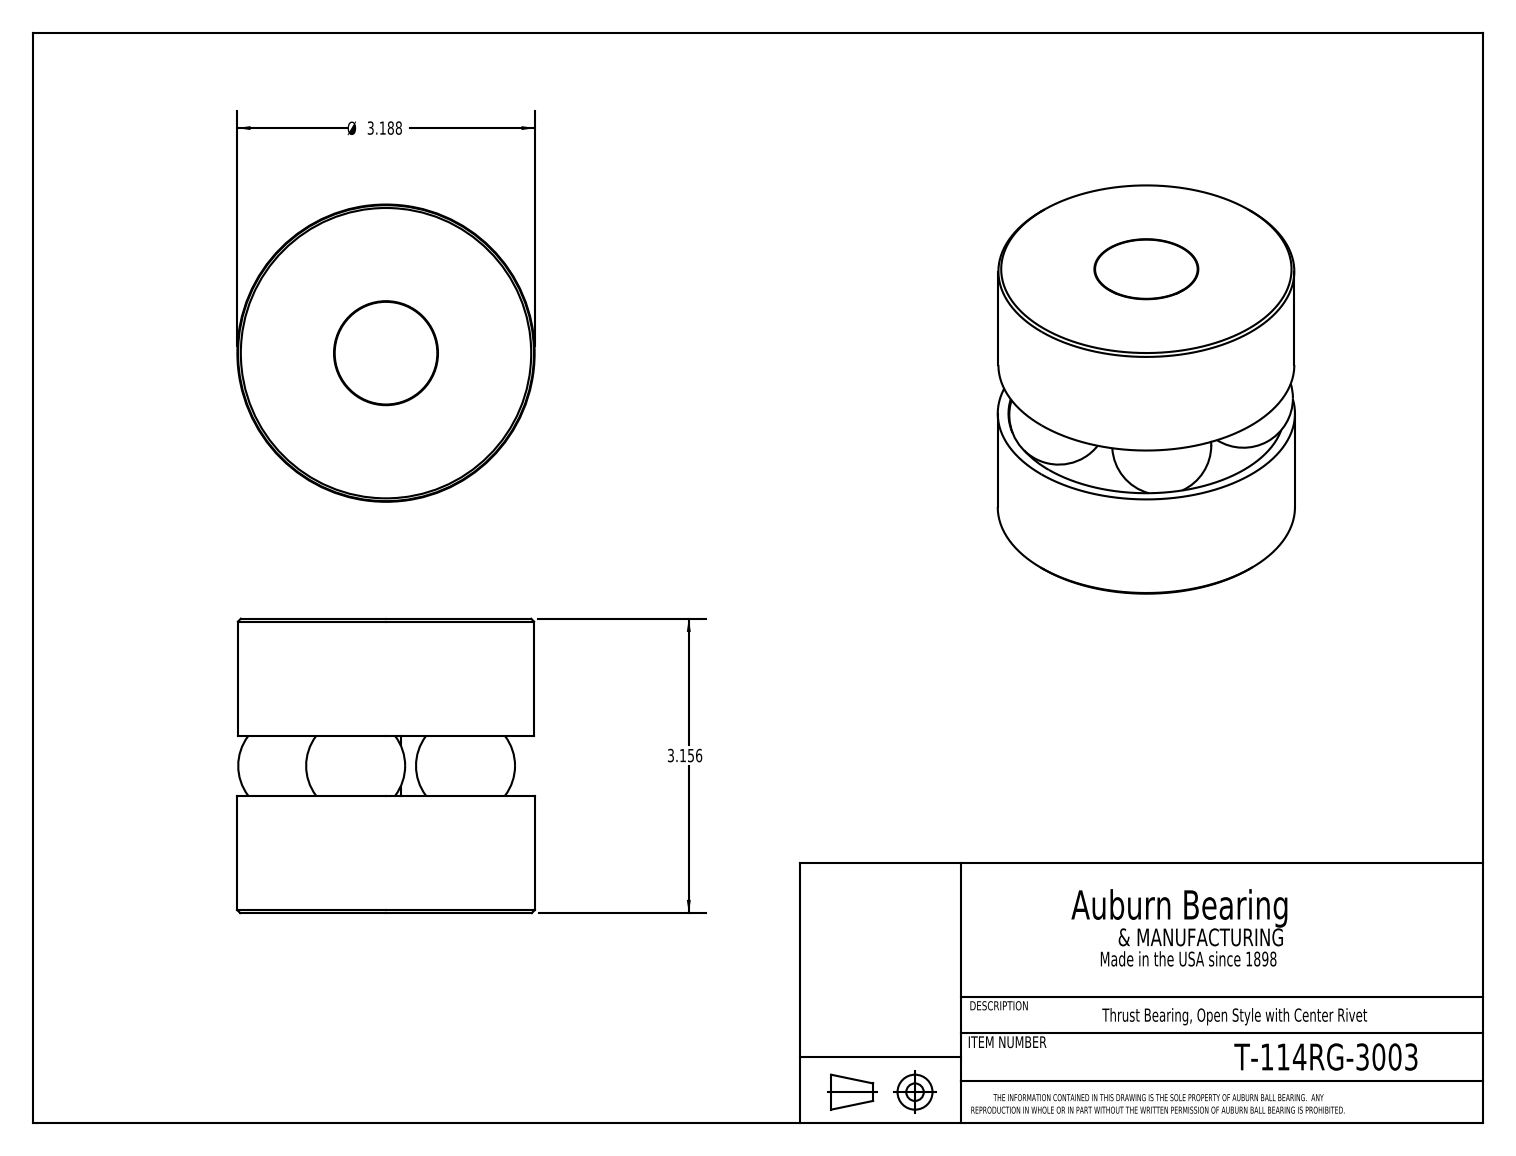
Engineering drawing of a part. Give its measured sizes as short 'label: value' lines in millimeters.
name: T-114RG_T-114RG-3003
written by: SolidWorks 2016 (CONFIG_CONTROL_DESIGN)
unit: mm
bodies: 8 solids, 26 faces (8 planar, 5 cylindrical, 13 other)
size: 81 × 81 × 80.2
volume: 352 300 mm³; area: 54 830 mm²
holes: 1× ⌀8.2
bosses: 1× ⌀81, 1× ⌀80.6, 1× ⌀7.9
face distances: 80.2, 32, 48.2, 16.2
